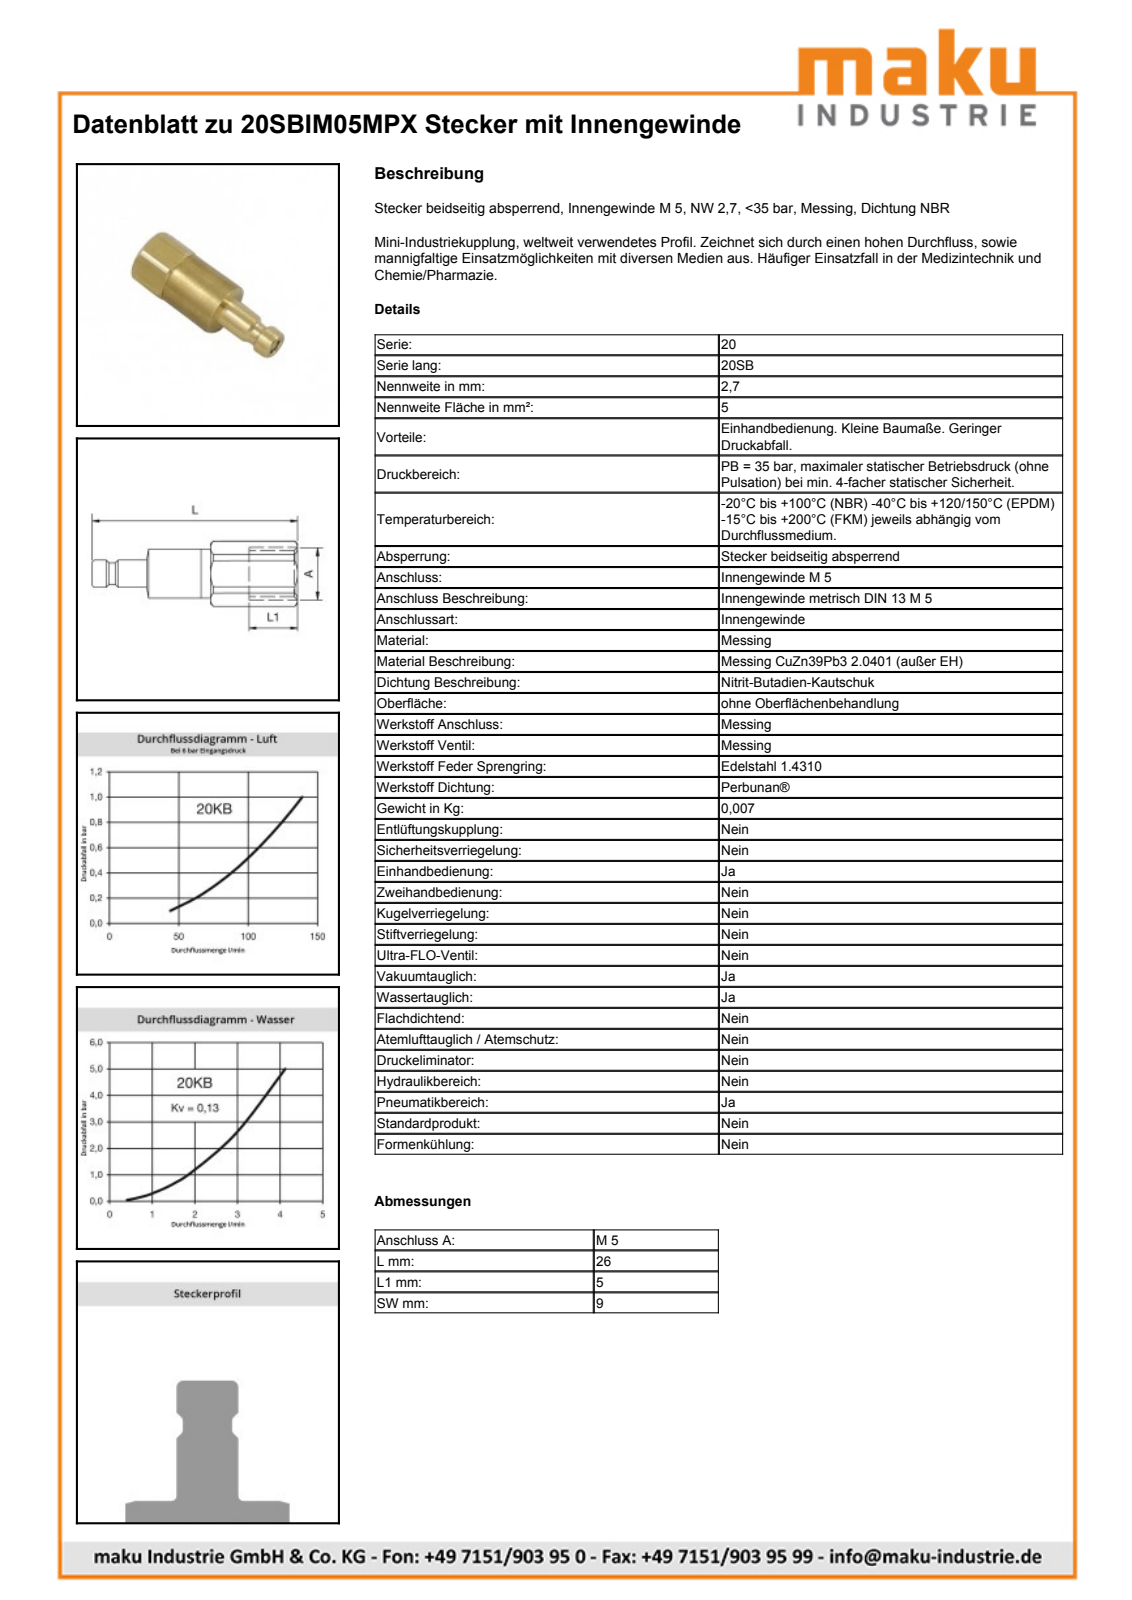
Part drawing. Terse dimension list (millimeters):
name: D114432
written by: Autodesk Inventor 2013 (AUTOMOTIVE_DESIGN)
unit: mm
bodies: 1 solid, 53 faces (12 planar, 17 cylindrical, 24 other)
size: 26.55 × 9.87 × 9.58
volume: 1 137 mm³; area: 1 012 mm²
holes: 1× ⌀6, 1× ⌀8, 1× ⌀8.1
bosses: 1× ⌀9, 1× ⌀7.3, 1× ⌀6.8, 1× ⌀5, 1× ⌀3.95
rounds: 1× R4.95
face distances: 9, 5.05, 1.5, 6.55, 20, 21.5, 26.55, 15.55, 4.45, 5.95
